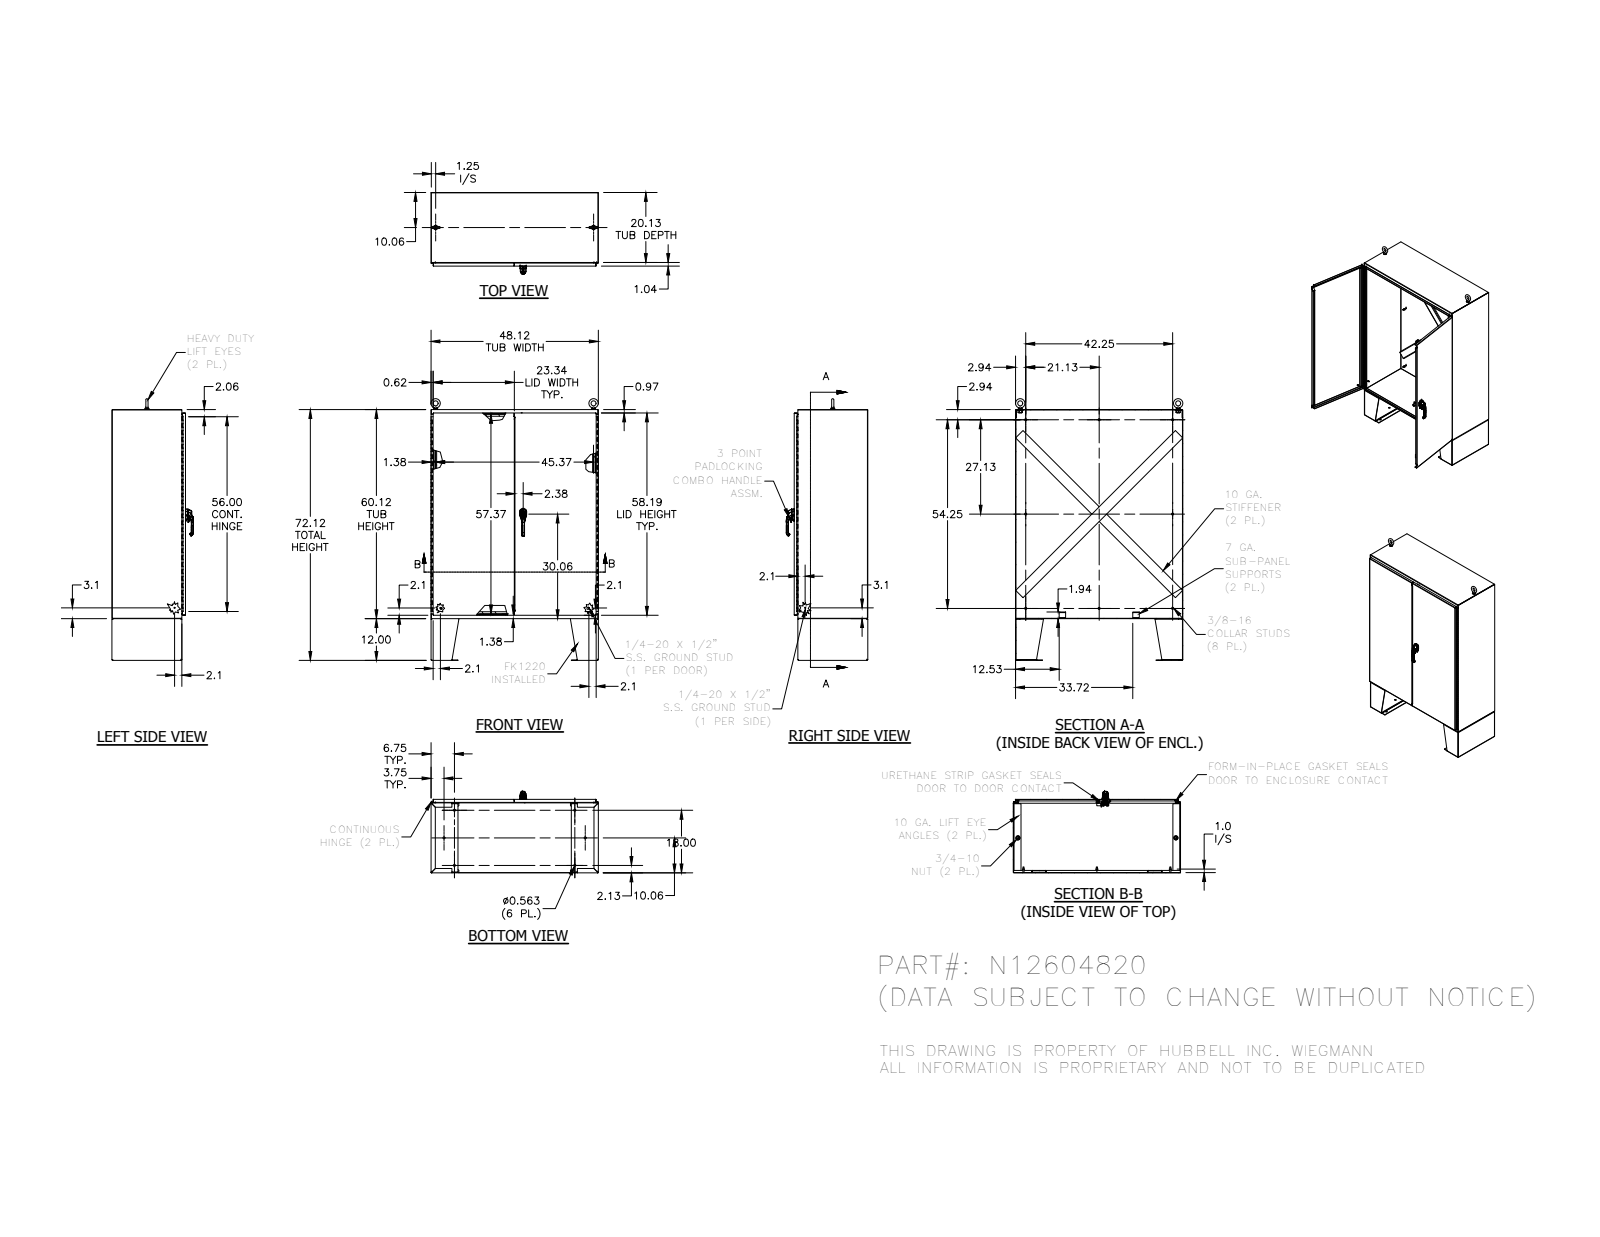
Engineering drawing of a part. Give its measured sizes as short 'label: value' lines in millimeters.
name: N12604820
written by: SolidWorks 2018 (AUTOMOTIVE_DESIGN)
unit: mm
bodies: 76 solids, 2392 faces (1384 planar, 708 cylindrical, 300 other)
size: 1911.3 × 1222.4 × 592.8
volume: 22 070 000 mm³; area: 17 350 000 mm²
holes: 18× ⌀14.3, 8× ⌀7, 4× ⌀5.1, 3× ⌀7.1, 2× ⌀3.2, 2× ⌀6.1, 2× ⌀6.4, 2× ⌀6.4, 2× ⌀10.2, 2× ⌀11.4, 2× ⌀16.3, 2× ⌀20.7
bosses: 8× ⌀8.4, 5× ⌀6.4, 4× ⌀15.9, 4× ⌀15.9, 3× ⌀8.6, 2× ⌀31.8, 2× ⌀28.4, 2× ⌀25.4
rounds: 24× R0.8, 23× R2.4, 22× R5.6, 18× R1.3, 16× R0.6, 15× R3.2, 13× R0.8, 8× R1.7
face distances: 2.4, 535.1, 532.7, 537.5, 1220, 1524.8, 1222.4, 1217.6, 3.2, 1522.4
hole spacings: 51.8, 127, 428.7, 476.3, 492.9, 873.9, 977.6, 978.7
